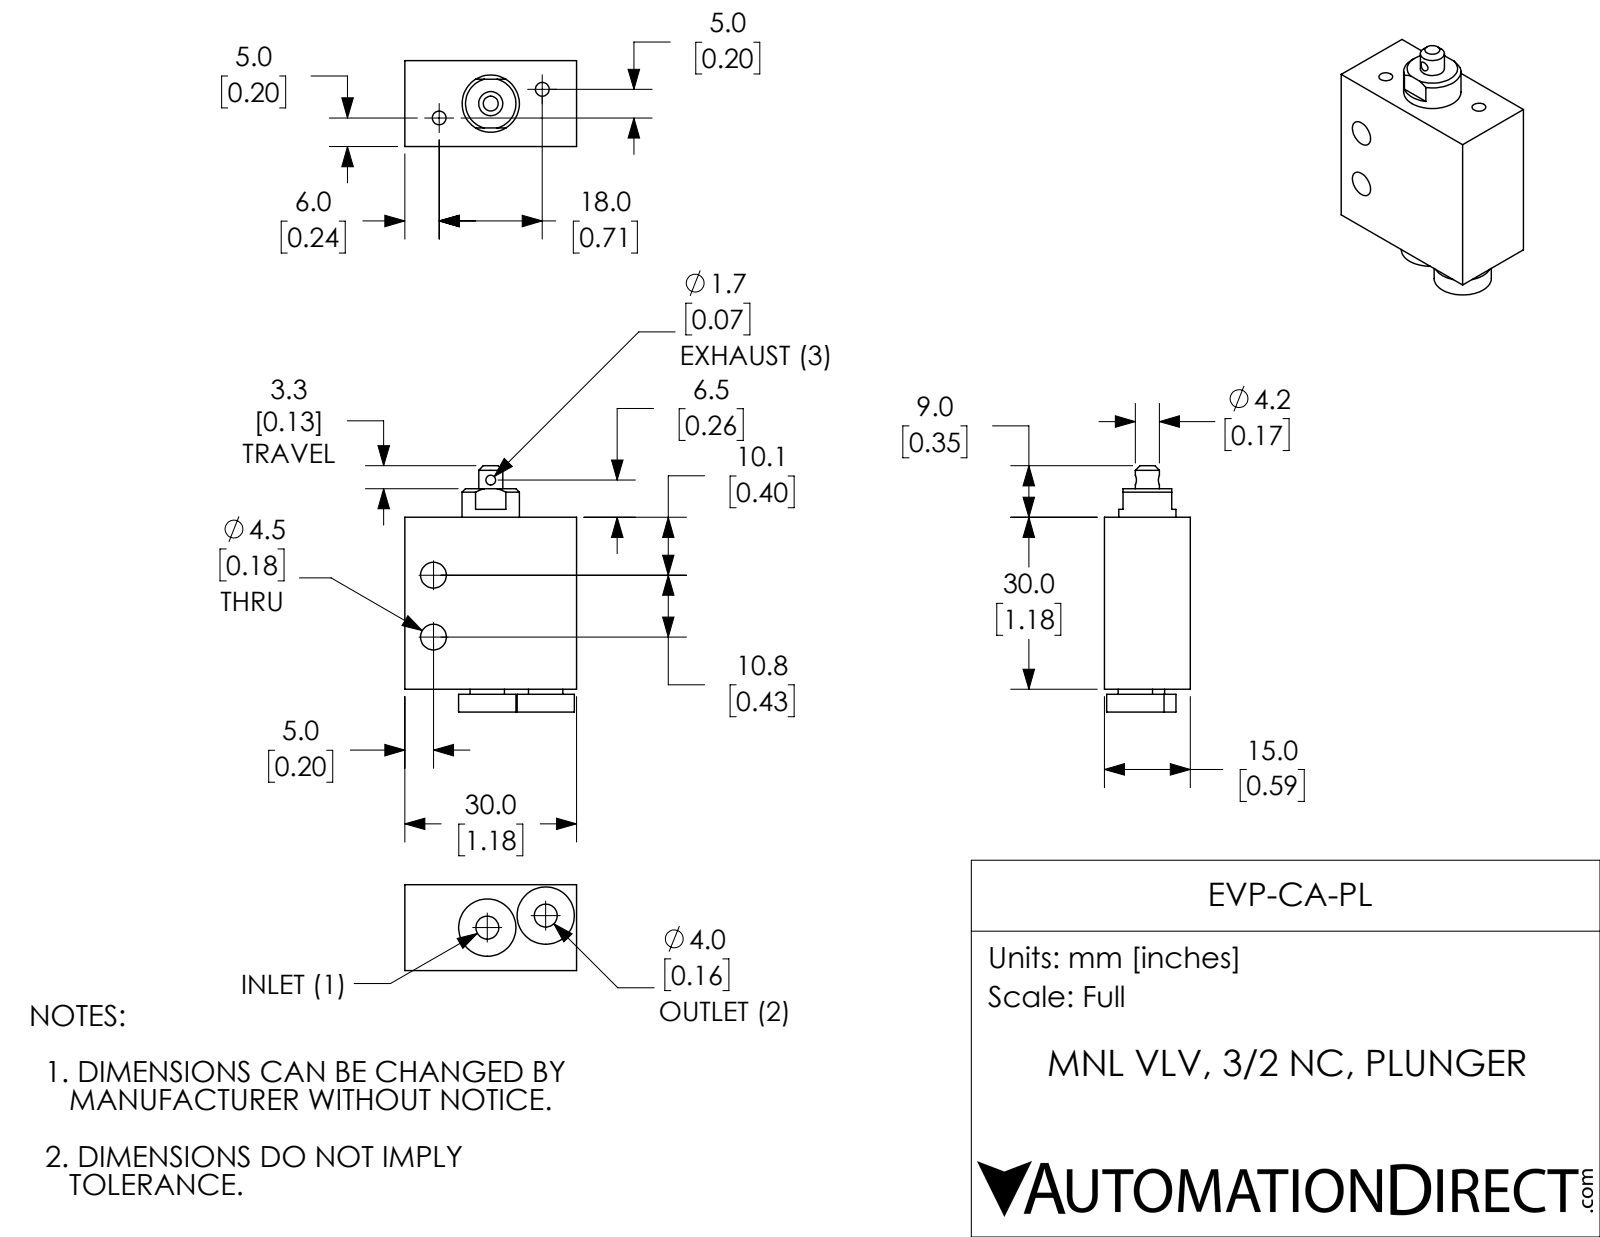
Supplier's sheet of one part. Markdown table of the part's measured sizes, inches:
| quantity | value |
| --- | --- |
| part name | EVP-CA-PL |
| STEP written by | SolidWorks 2017 (AUTOMOTIVE_DESIGN) |
| units | inches |
| bodies | 1 solid, 50 faces (20 planar, 26 cylindrical, 4 other) |
| overall size | 1.693 × 1.181 × 0.591 |
| volume | 0.844 in³ |
| surface area | 7.378 in² |
| round holes (diameter × count) | 0.094 × 2, 0.157 × 2, 0.177 × 2, 0.067 × 1 |
| round bosses / shafts (diameter × count) | 0.394 × 3, 0.236 × 2, 0.165 × 1 |
| main face-to-face distances | 0.591, 1.181, 0.157, 1.339, 0.122, 0.035, 1.217, 1.535, 1.413, 1.378 |
| hole center spacings | 0.183, 0.345, 0.391, 0.41, 0.425, 0.732, 0.735, 0.763 |
